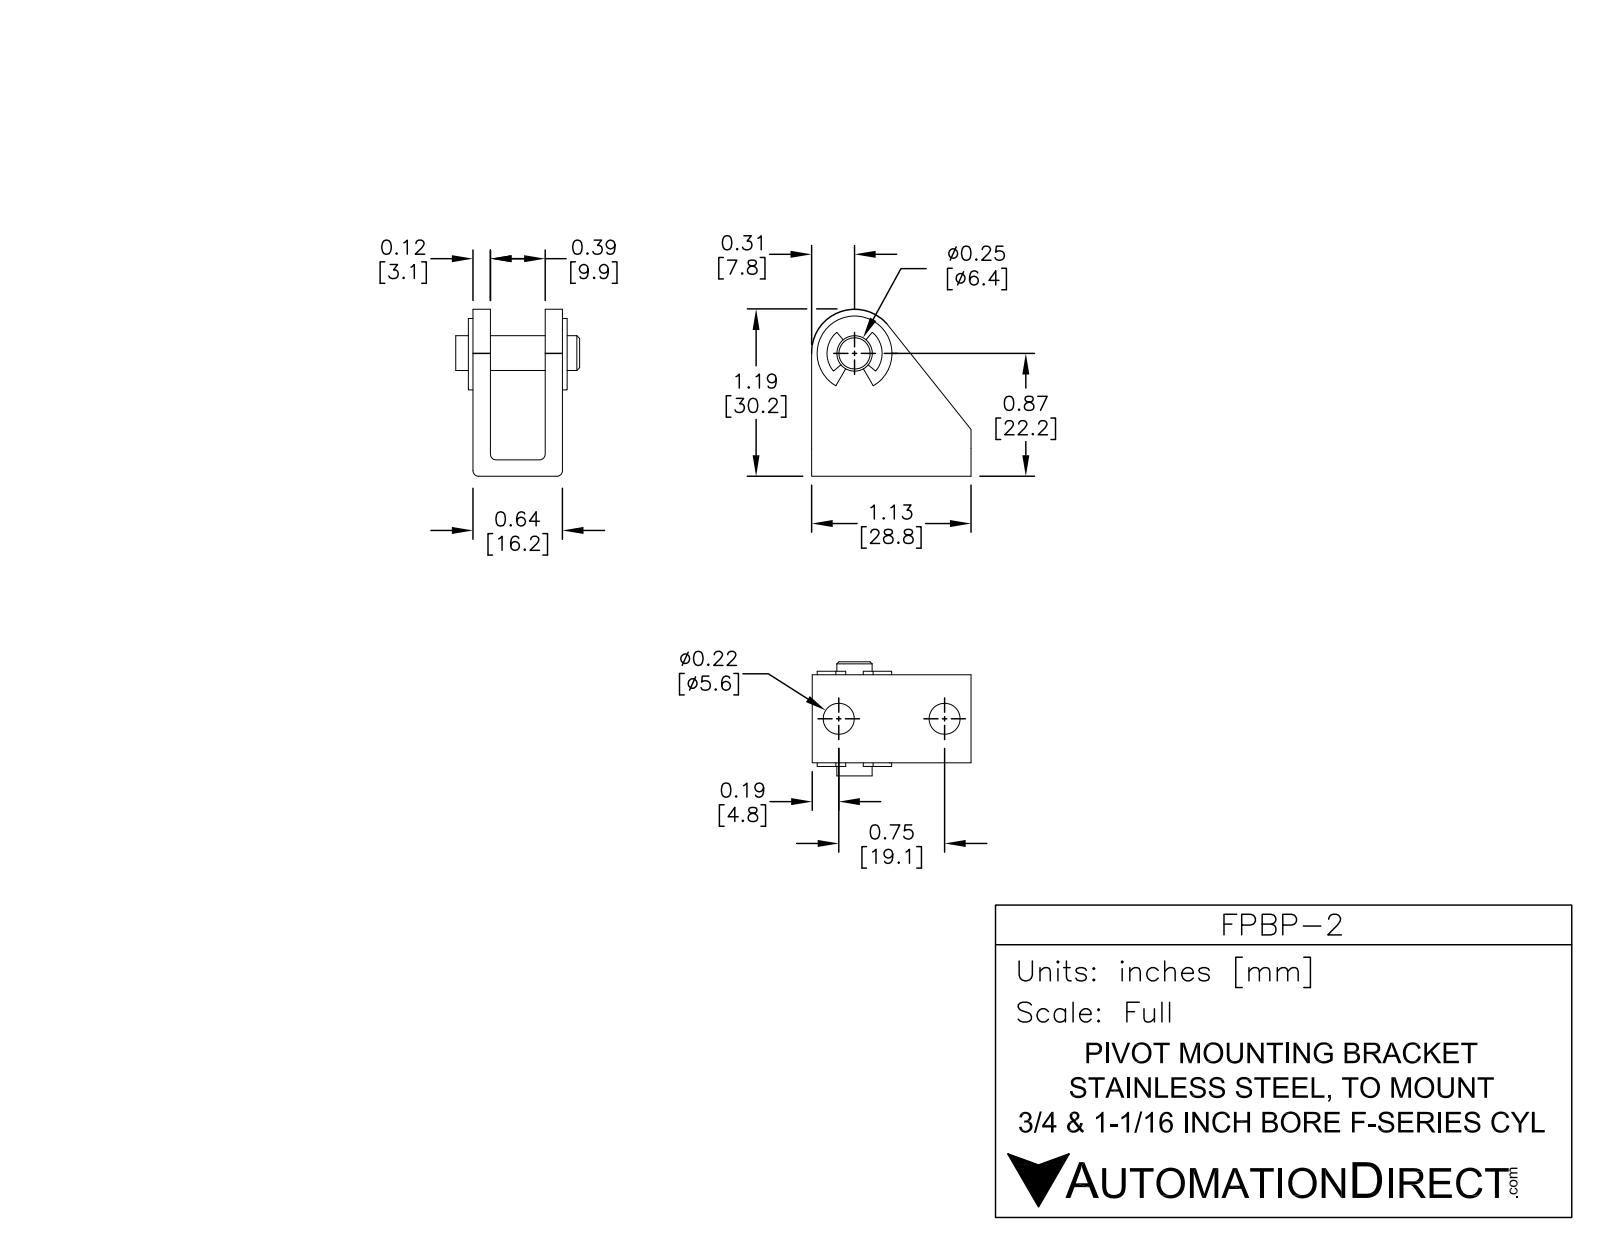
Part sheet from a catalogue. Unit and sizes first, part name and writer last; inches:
Units: inches
Overall size (bounding box): 1.189 × 1.134 × 0.882
Round holes (diameter × count): ⌀0.22 ×2, ⌀0.25 ×1
Partial cylindrical surfaces — rounded edges, fillets, slot ends (radius × count): R0.03 ×2, R0.152 ×2, R0.307 ×1
Main face-to-face distances: 0.122, 0.518, 0.64, 0.396, 1.134, 0.121, 0.243, 0.639, 0.761, 0.882
Hole centre spacings: 0.75
Volume: 0.319 in³ · Surface area: 6.453 in²
Bodies: 2 solids, 36 faces (20 planar, 16 cylindrical, 0 other)
Part name (STEP PRODUCT): FPBP-2
STEP written by: SolidWorks 2017 (AUTOMOTIVE_DESIGN)
